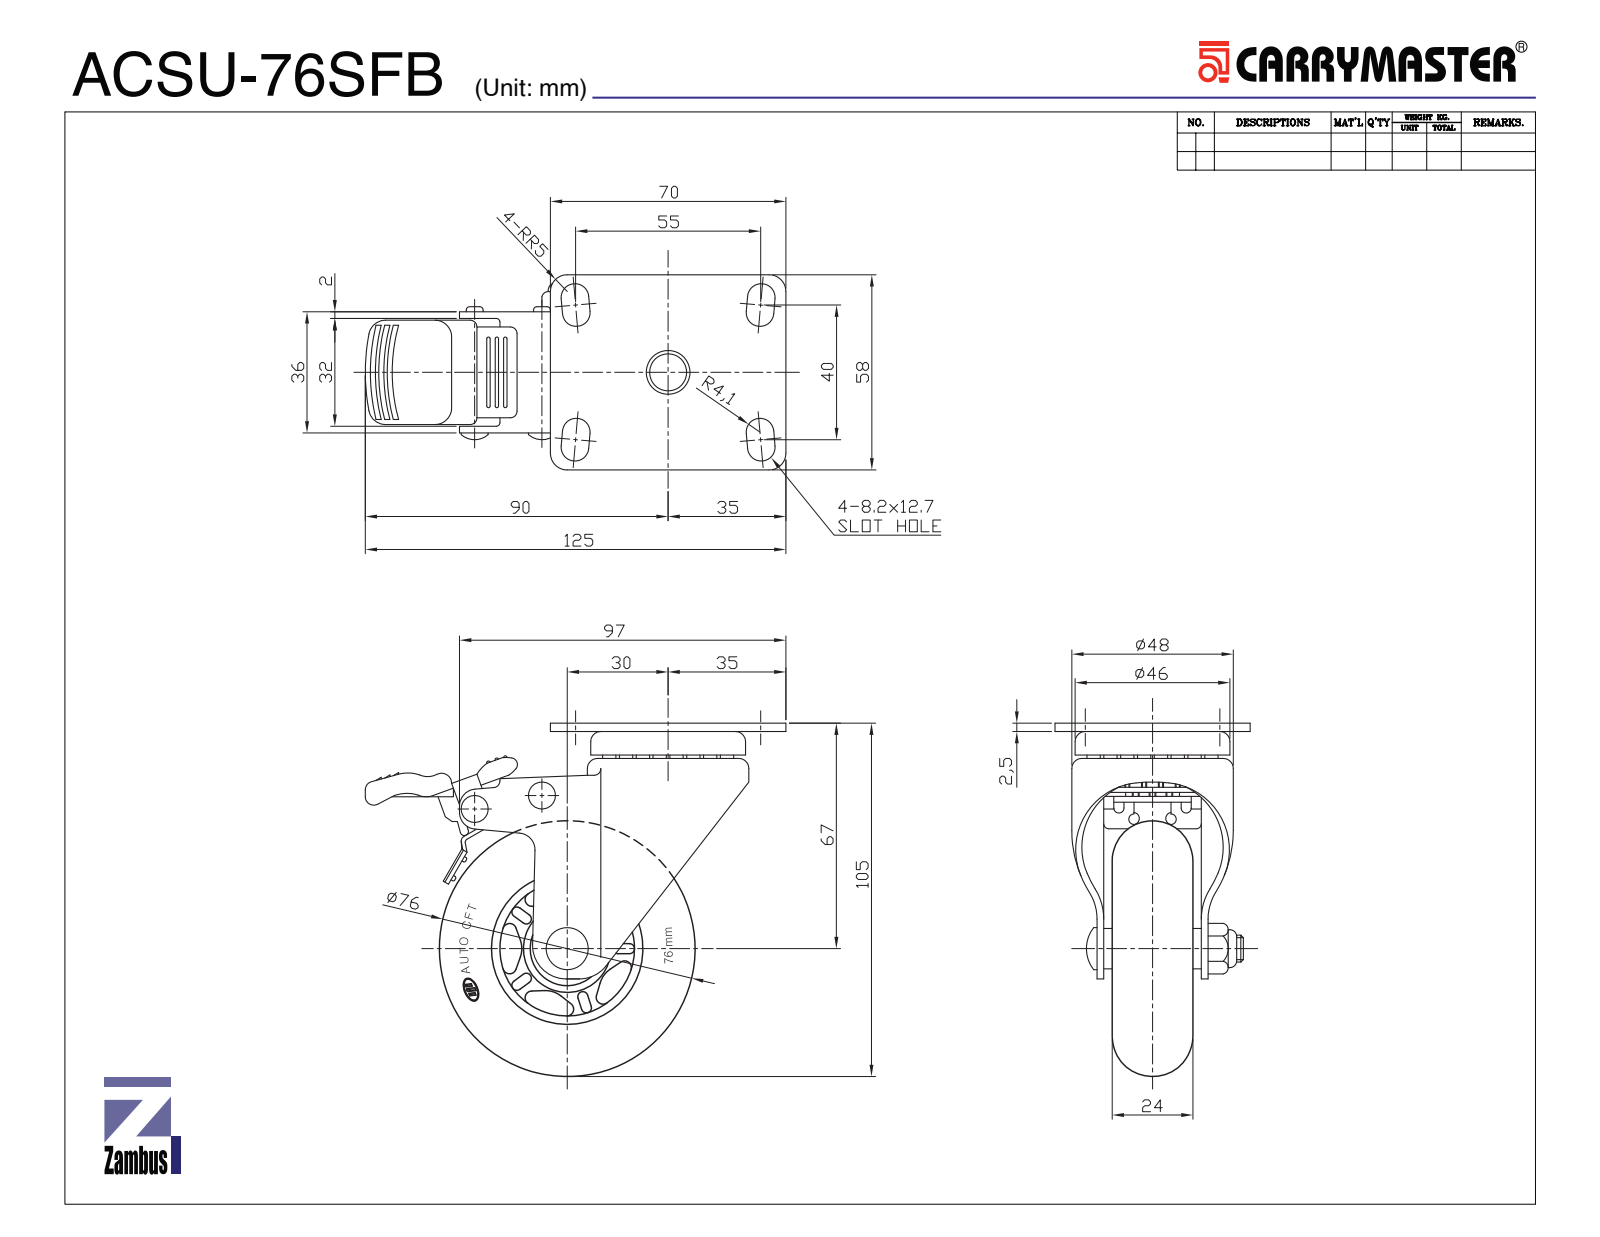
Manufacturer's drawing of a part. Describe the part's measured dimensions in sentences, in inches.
The part is named "ACSU-76SFB". Its 3-D file was written by "SolidWorks 2015 (CONFIG_CONTROL_DESIGN)". It is 19 solids with 1060 faces: 386 planar, 439 cylindrical and 235 other. Overall it measures 4.922 by 4.13 by 2.283 inches. Its volume is 8.647 cubic inches and its surface area 134.2 square inches. Round holes: 2 of diameter 0.138, 2 of diameter 0.157, 1 of diameter 0.268, 1 of diameter 0.315, 1 of diameter 0.319, 1 of diameter 0.433, 1 of diameter 0.682, 1 of diameter 0.728, 1 of diameter 0.866, 1 of diameter 1.063, 1 of diameter 1.543, 1 of diameter 1.713. Round bosses or shafts: 2 of diameter 0.193, 1 of diameter 1.87, 1 of diameter 1.669, 1 of diameter 1.193, 1 of diameter 0.709, 1 of diameter 0.63, 1 of diameter 0.499, 1 of diameter 0.492. Partial cylindrical surfaces (rounded edges, fillets, slot ends): 53 of radius 0.039, 44 of radius 0.03, 28 of radius 0.059, 26 of radius 0.049, 22 of radius 0.02, 12 of radius 0.079, 9 of radius 0.118, 8 of radius 0.161. The main face-to-face distances are 0.079, 0.098, 1.398, 0.138, 0.059, 0.266, 1.211, 0.187, 1.132, 1.476. The hole center spacings are 0.824, 1.77, 1.91.
